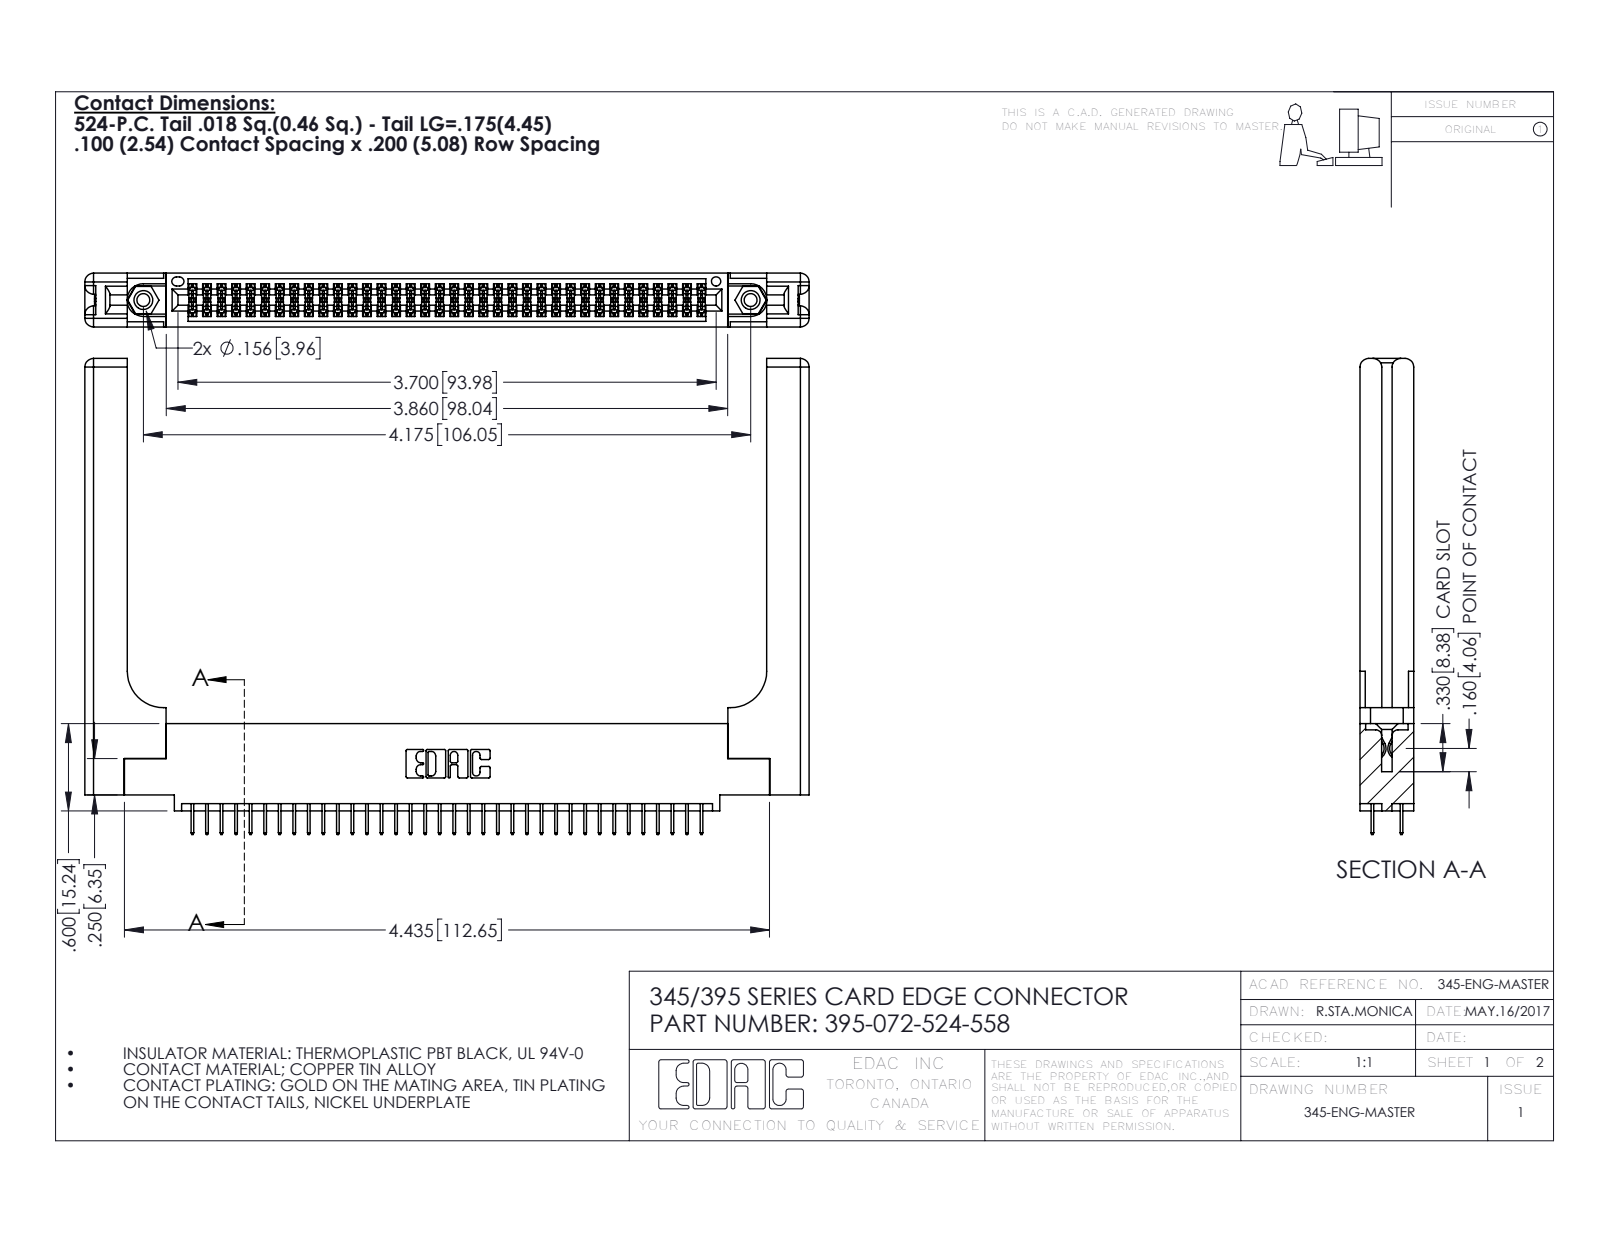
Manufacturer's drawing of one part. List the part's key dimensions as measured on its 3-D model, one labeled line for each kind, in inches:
Part name (STEP PRODUCT): 345 Part_0.110 Offset - 0.156 Dia-TH; 345-292-001_345-293-124; 395-072-524-558; 345-220-058_345-220-058 (+1 more)
STEP written by: SolidWorks 2016 (CONFIG_CONTROL_DESIGN)
Units: inches
Bodies: 77 solids, 4274 faces (3040 planar, 1174 cylindrical, 60 other)
Overall size (bounding box): 4.979 × 3.272 × 0.37
Volume: 1.252 in³ · Surface area: 34.96 in²
Round holes (diameter × count): ⌀0.089 ×2, ⌀0.125 ×2, ⌀0.156 ×2, ⌀0.064 ×1
Round bosses / shafts (diameter × count): ⌀0.155 ×2
Partial cylindrical surfaces — rounded edges, fillets, slot ends (radius × count): R0.006 ×108, R0.01 ×22, R0.06 ×16, R0.007 ×6, R0.031 ×6, R0.026 ×3, R0.014 ×2, R0.019 ×2
Main face-to-face distances: 0.37, 0.072, 0.298, 0.2, 0.098, 0.272, 0.025, 0.225, 0.148, 0.15
Hole centre spacings: 0.27, 3.939, 4.175
